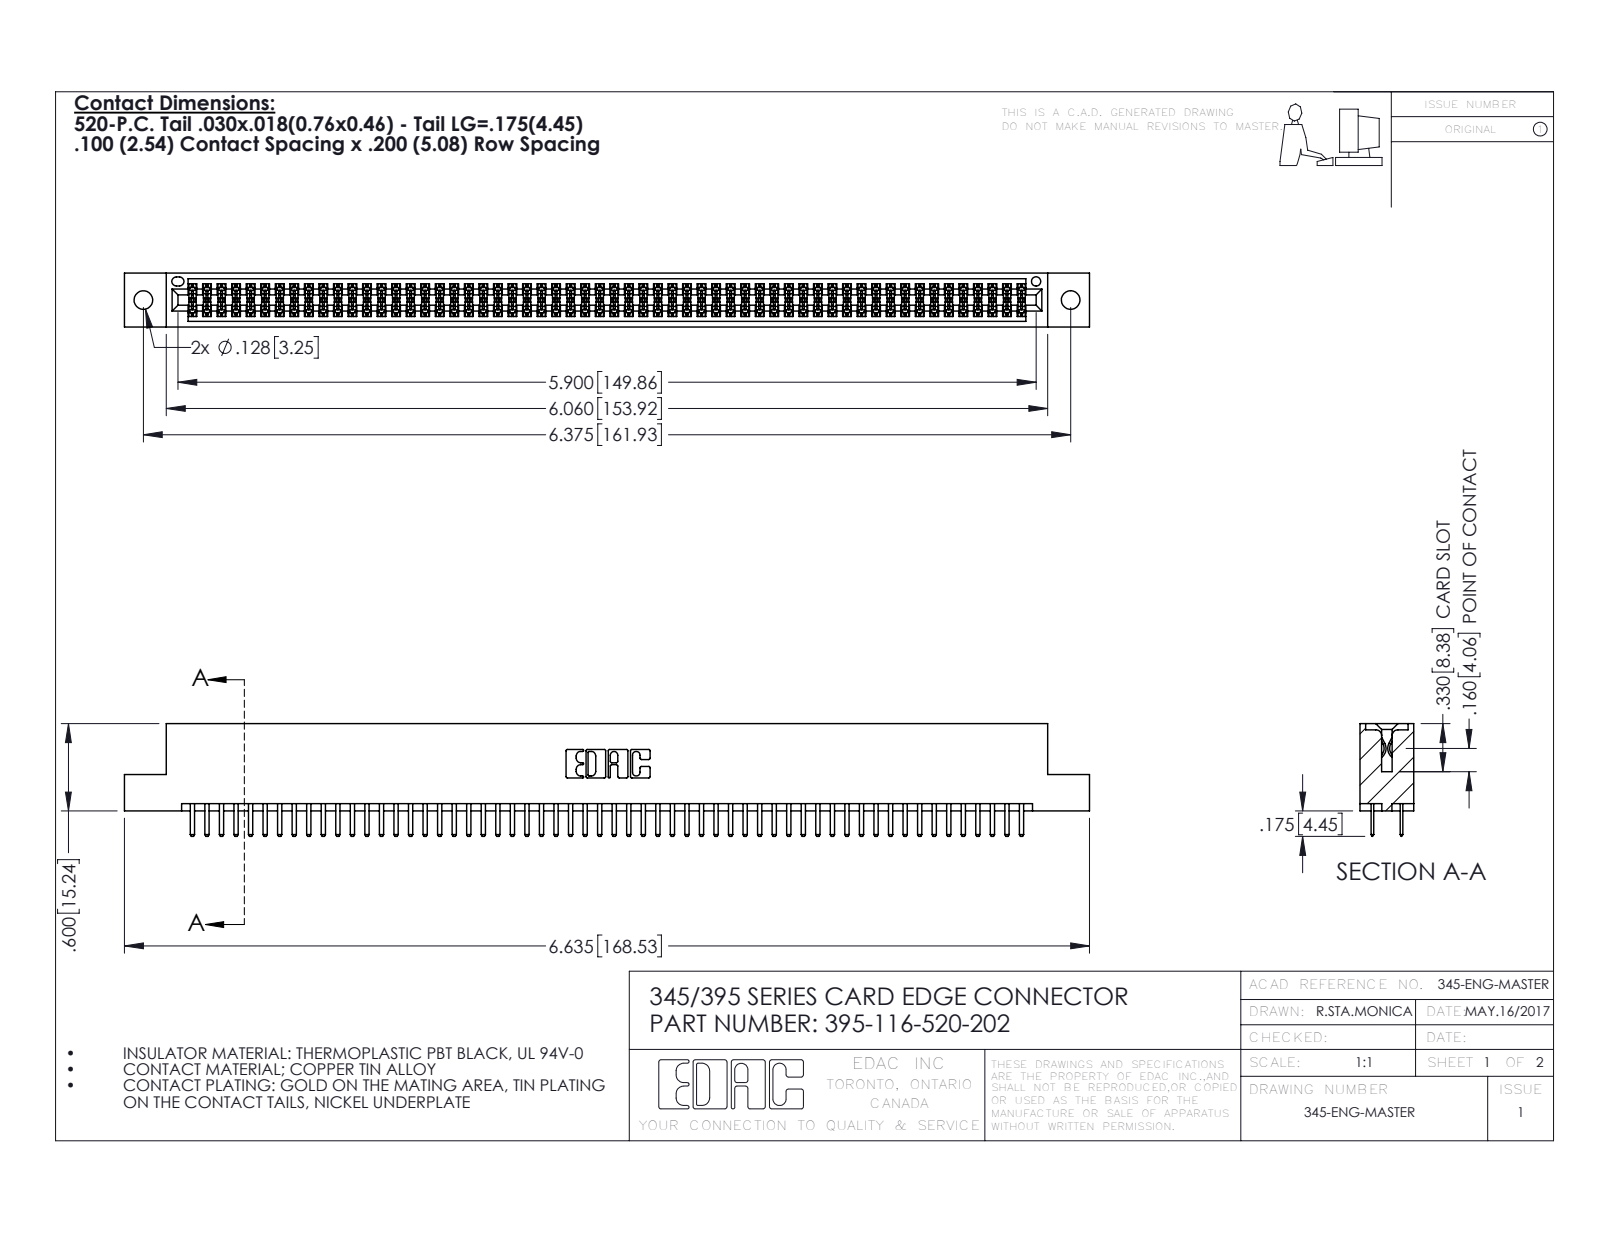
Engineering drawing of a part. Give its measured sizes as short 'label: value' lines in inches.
name: 345 Part_Flush Mounting Lugs - 0.128 Dia; 345-292-001_345-293-120; 395-116-520-202
written by: SolidWorks 2016 (CONFIG_CONTROL_DESIGN)
unit: in
bodies: 117 solids, 6390 faces (4140 planar, 2250 cylindrical, 0 other)
size: 6.635 × 0.775 × 0.37
volume: 1.003 in³; area: 37.54 in²
holes: 2× ⌀0.128, 1× ⌀0.064
rounds: 174× R0.006, 120× R0.01, 22× R0.01, 6× R0.007, 6× R0.031, 3× R0.026, 2× R0.014, 2× R0.019
face distances: 0.298, 0.072, 0.2, 0.37, 0.098, 0.272, 0.025, 0.225, 0.022, 0.072
hole spacings: 0.27, 6.139, 6.375
